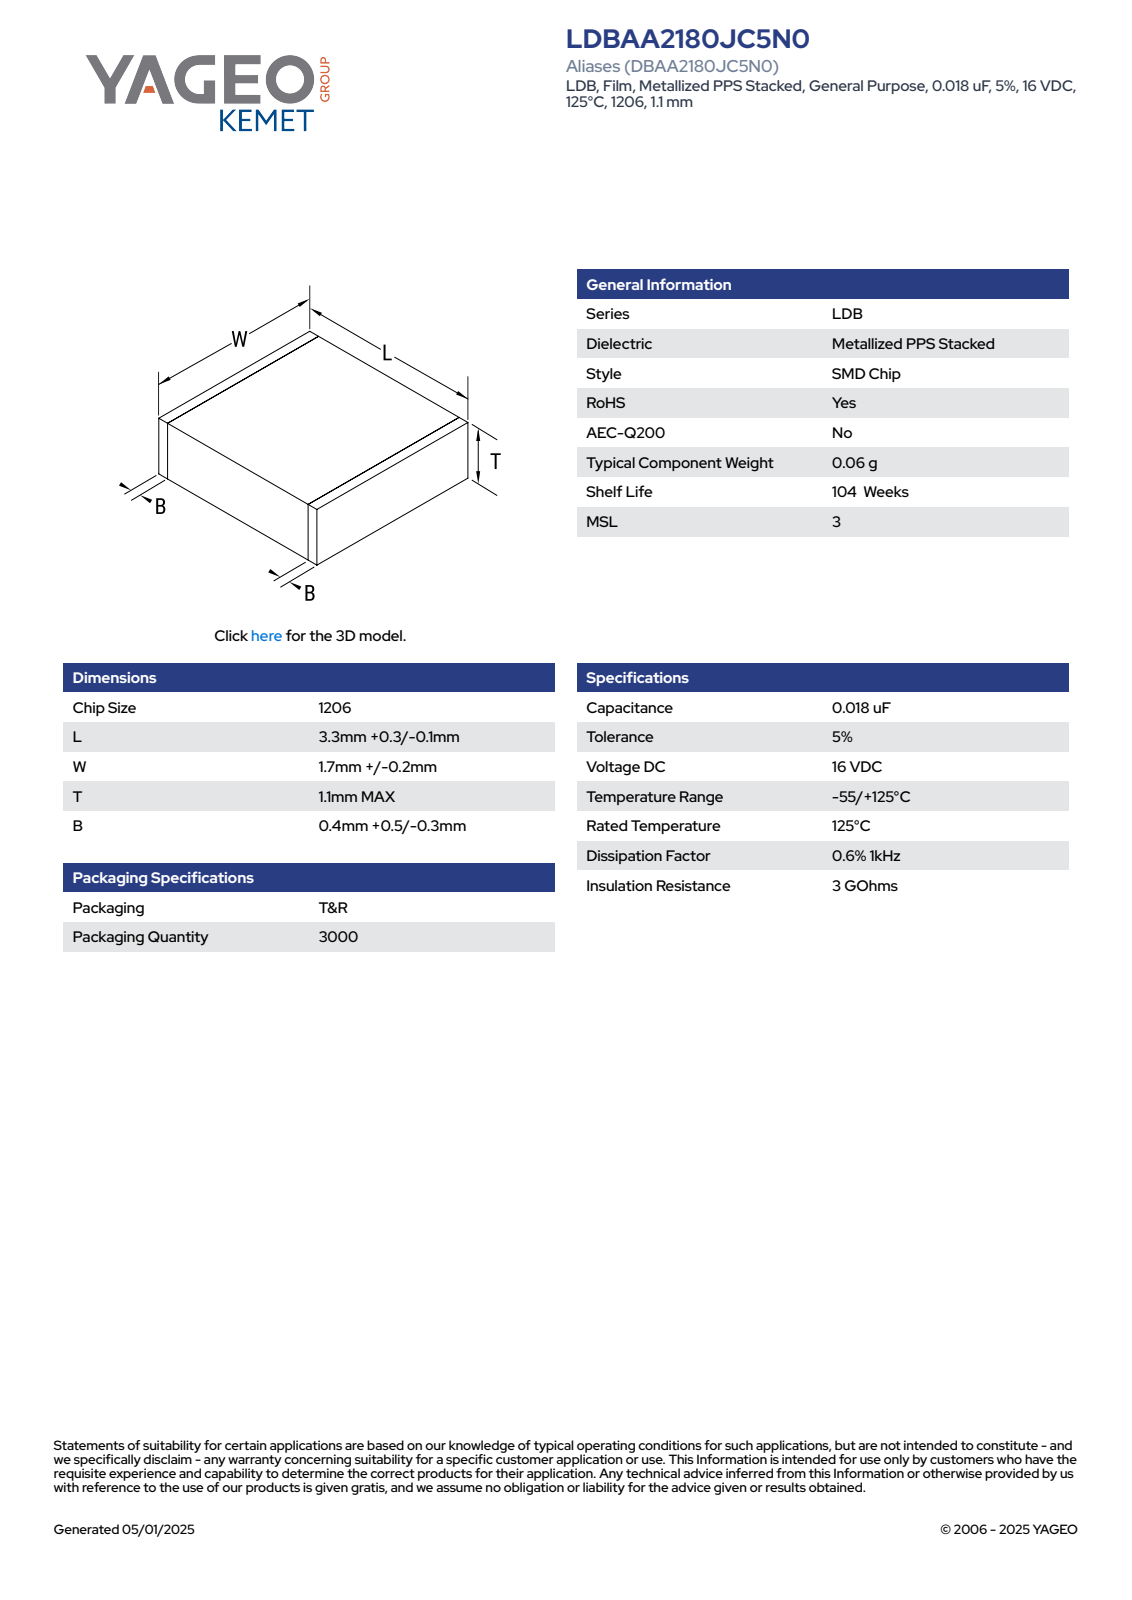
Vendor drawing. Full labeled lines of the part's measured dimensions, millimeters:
Part name (STEP PRODUCT): CFS_LDELDB_1206_L3.6W1.9T1.1B0.9
STEP written by: SolidWorks 2020 (AUTOMOTIVE_DESIGN)
Units: millimetres
Bodies: 4 solids, 73 faces (73 planar, 0 cylindrical, 0 other)
Overall size (bounding box): 3.6 × 1.9 × 1.1
Volume: 7 mm³ · Surface area: 26 mm²
Main face-to-face distances: 1.08, 1.09, 1.88, 1.89, 3.6, 1.1, 1.9, 0.5, 3.1, 2.6
